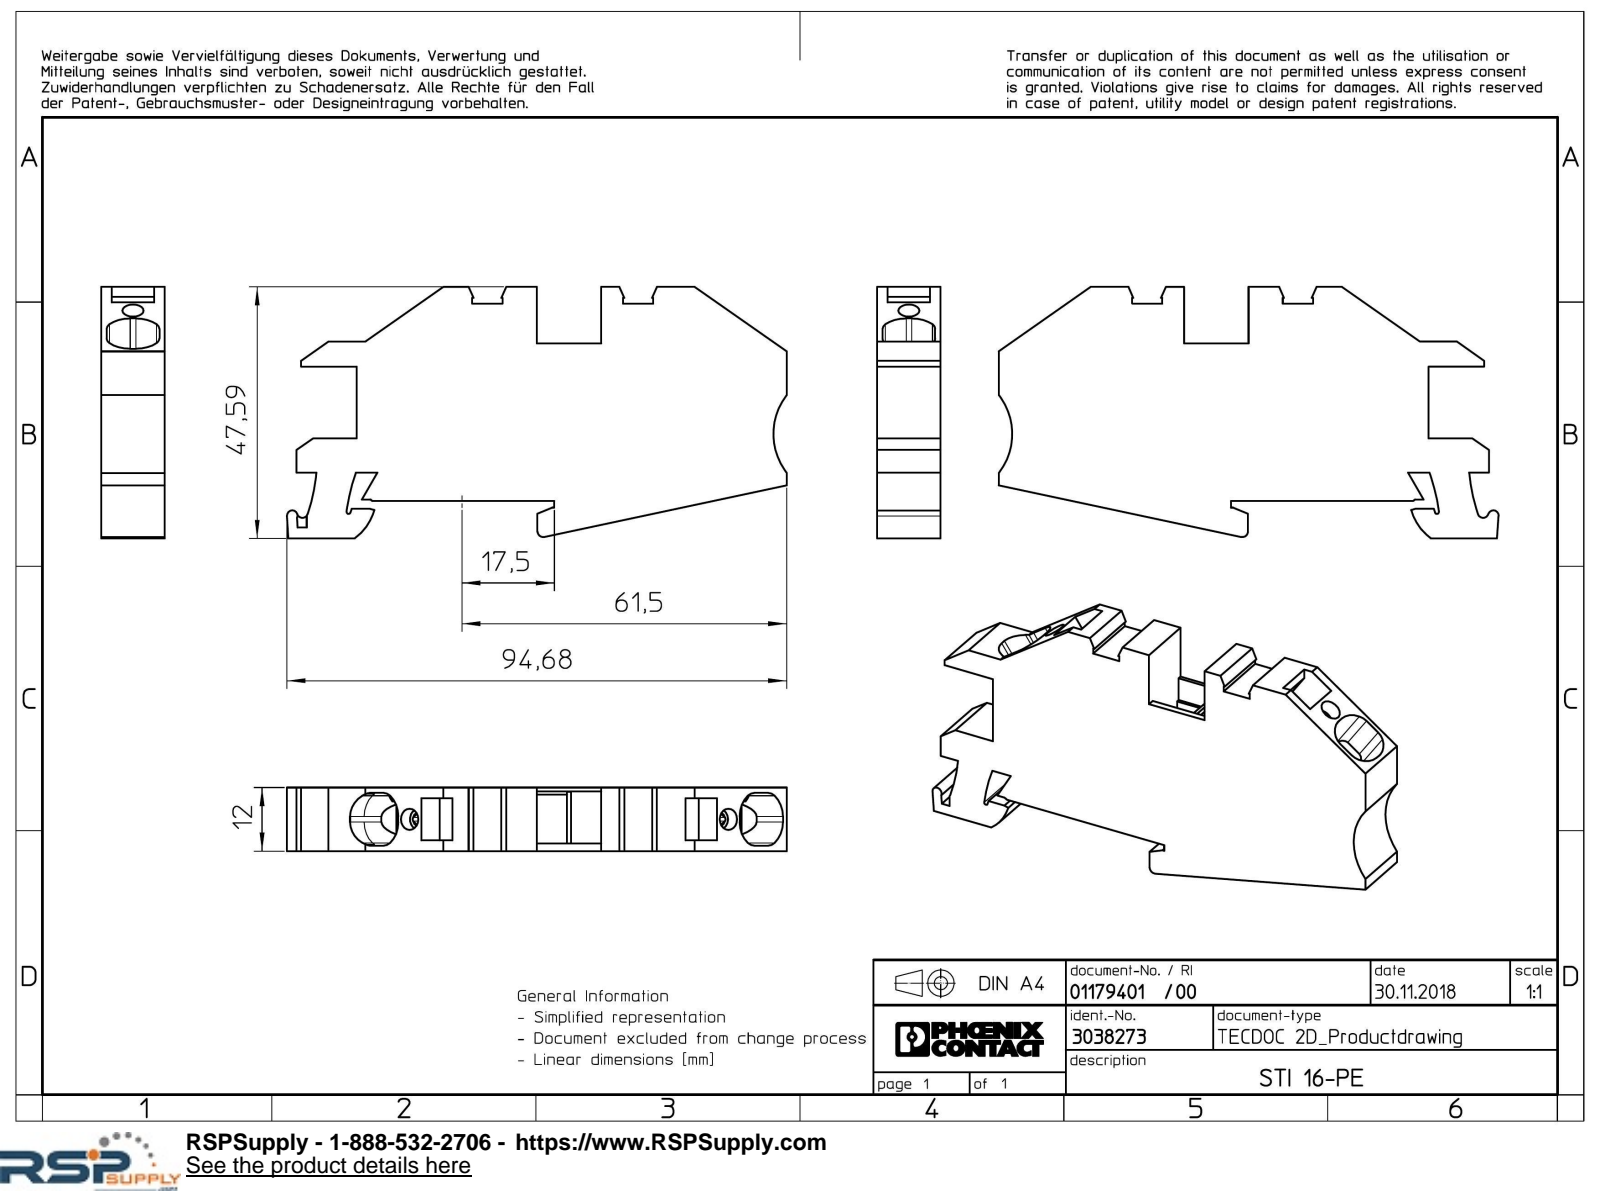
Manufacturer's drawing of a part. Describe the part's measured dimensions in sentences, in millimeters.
The part is named "STI_16-PE-SELECT". Its 3-D file was written by "Creo Elements/Direct Modeling 18.1I 14-Aug-2016 (C) Parametric Technology GmbH (AUTOMOTIVE_DESIGN)". It is 1 solid with 166 faces: 115 planar, 43 cylindrical and 8 other. Overall it measures 94.68 by 47.59 by 12 millimeters. Its volume is 33 094 cubic millimeters and its surface area 13 622 square millimeters. Round holes: 2 of diameter 4. Partial cylindrical surfaces (rounded edges, fillets, slot ends): 8 of radius 0.5, 8 of radius 2.5, 6 of radius 5, 2 of radius 0.3, 2 of radius 1, 2 of radius 35, 1 of radius 0.38, 1 of radius 1.04. The main face-to-face distances are 12, 10, 2, 1, 35.14, 7.6, 2.6, 9.4, 0.6, 12.2.
